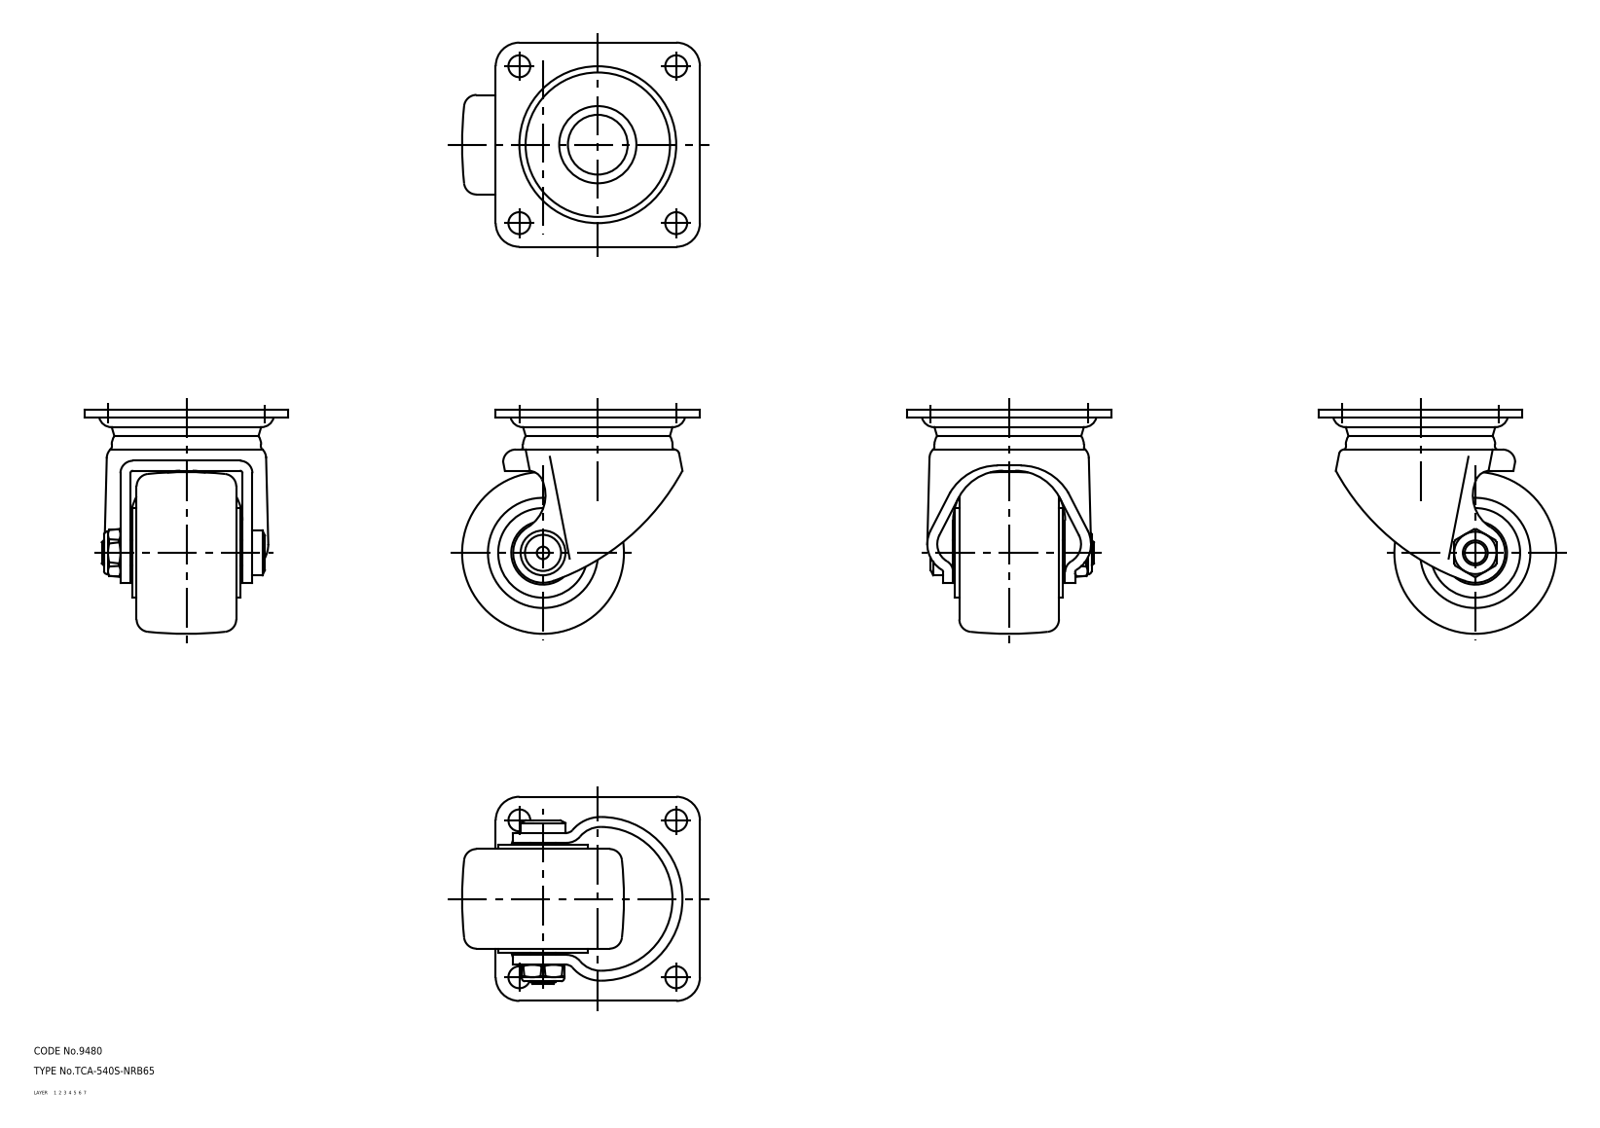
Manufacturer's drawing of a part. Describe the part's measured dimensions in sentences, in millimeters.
The part is named "main shaft; wheel; mounting plate; axle (+1 more)". Its 3-D file was written by "CADfix (AUTOMOTIVE_DESIGN)". It is 5 solids with 218 faces: 0 planar, 0 cylindrical and 218 other. Overall it measures 95.5 by 90 by 82 millimeters. Its volume is 225 178 cubic millimeters and its surface area 57 817 square millimeters.
